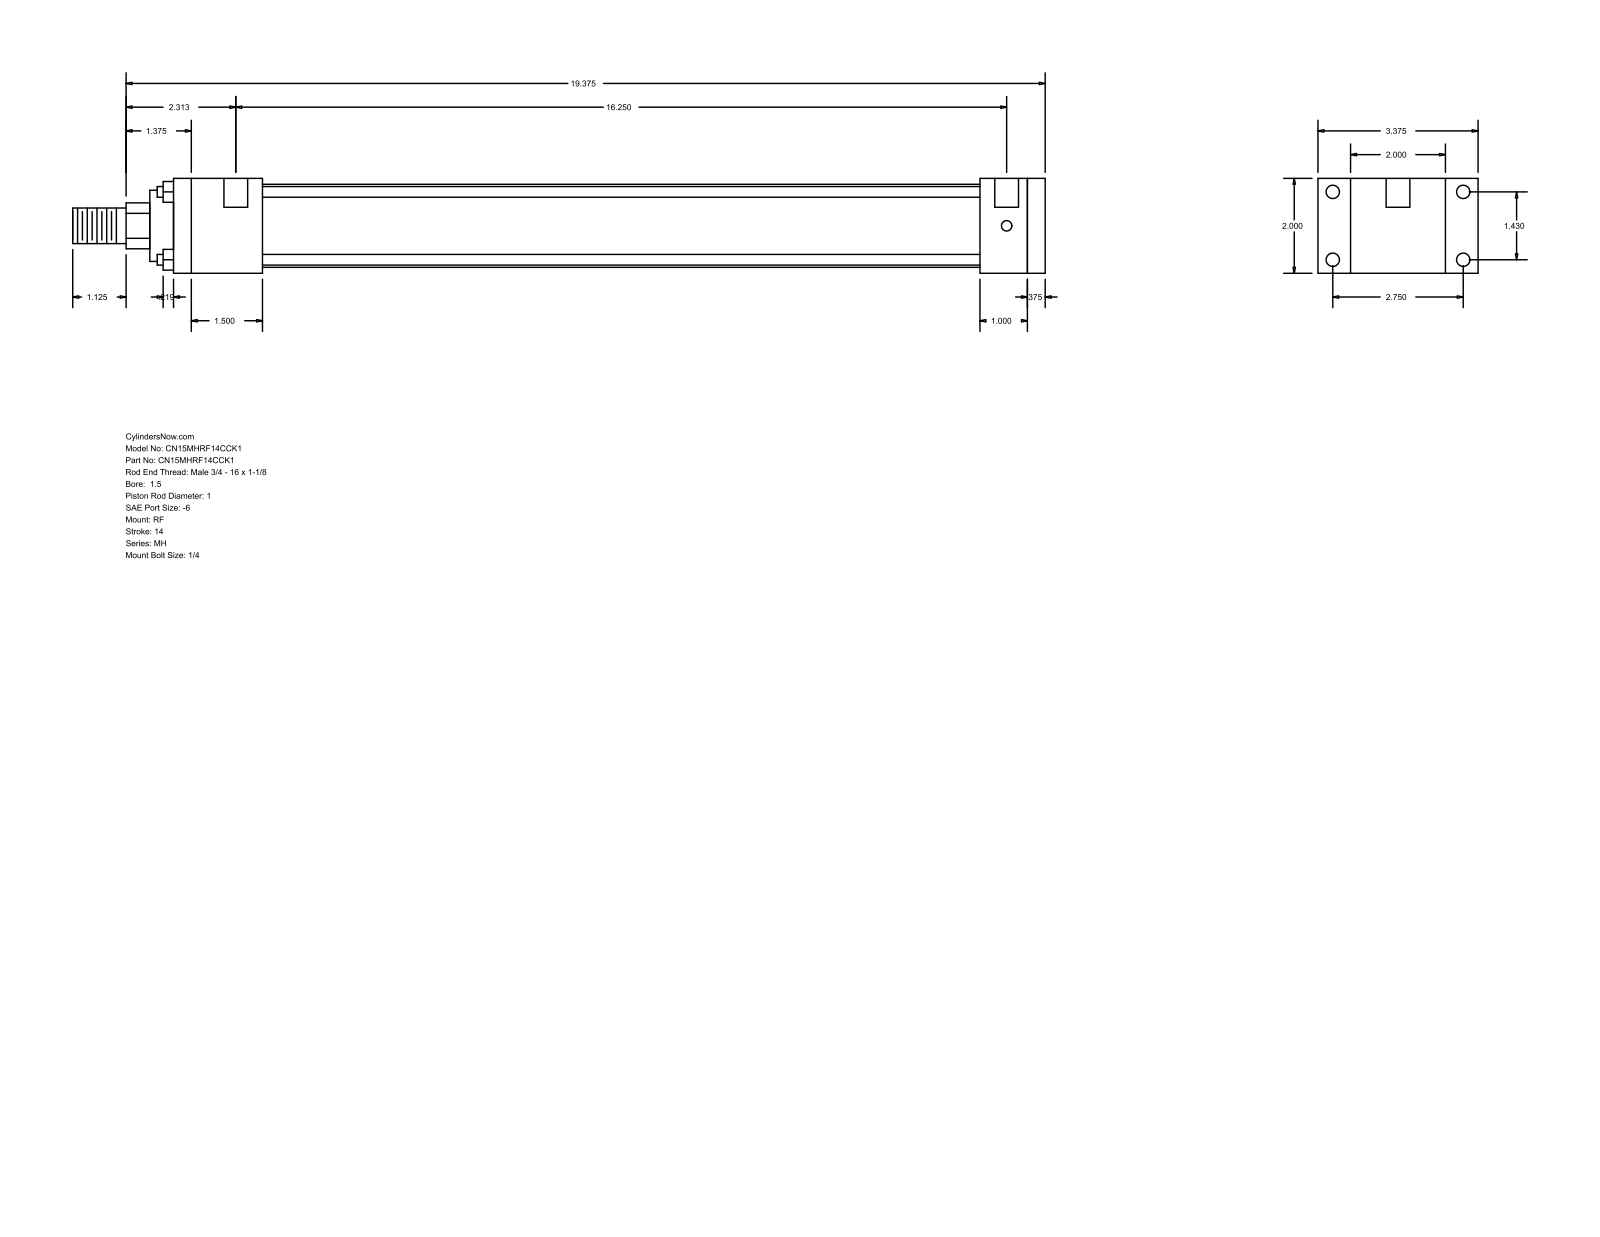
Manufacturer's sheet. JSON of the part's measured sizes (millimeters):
{"part_name": "MH_RF__0150_1", "step_written_by": "GSSL Pune (CONFIG_CONTROL_DESIGN)", "units": "millimeters", "bodies": {"solids": 0, "faces": 92, "planar": 64, "cylindrical": 28, "other": 0}, "overall_size": [520.7, 85.72, 50.8], "round_holes": [[5.56, 4], [7.14, 4], [12.7, 2]], "round_bosses_or_shafts": [[5.71, 4], [44.45, 1], [38.1, 1], [25.4, 1], [19.05, 1]], "partial_cylinders_radius": [[12.29, 1]], "face_to_face_distances": [50.8, 9.52, 457.2, 25.4, 466.72, 17.46, 68.26, 431.8, 34.92, 47.63], "hole_center_spacings": [36.32, 69.84, 78.72, 415.93, 3.18, 412.75]}
